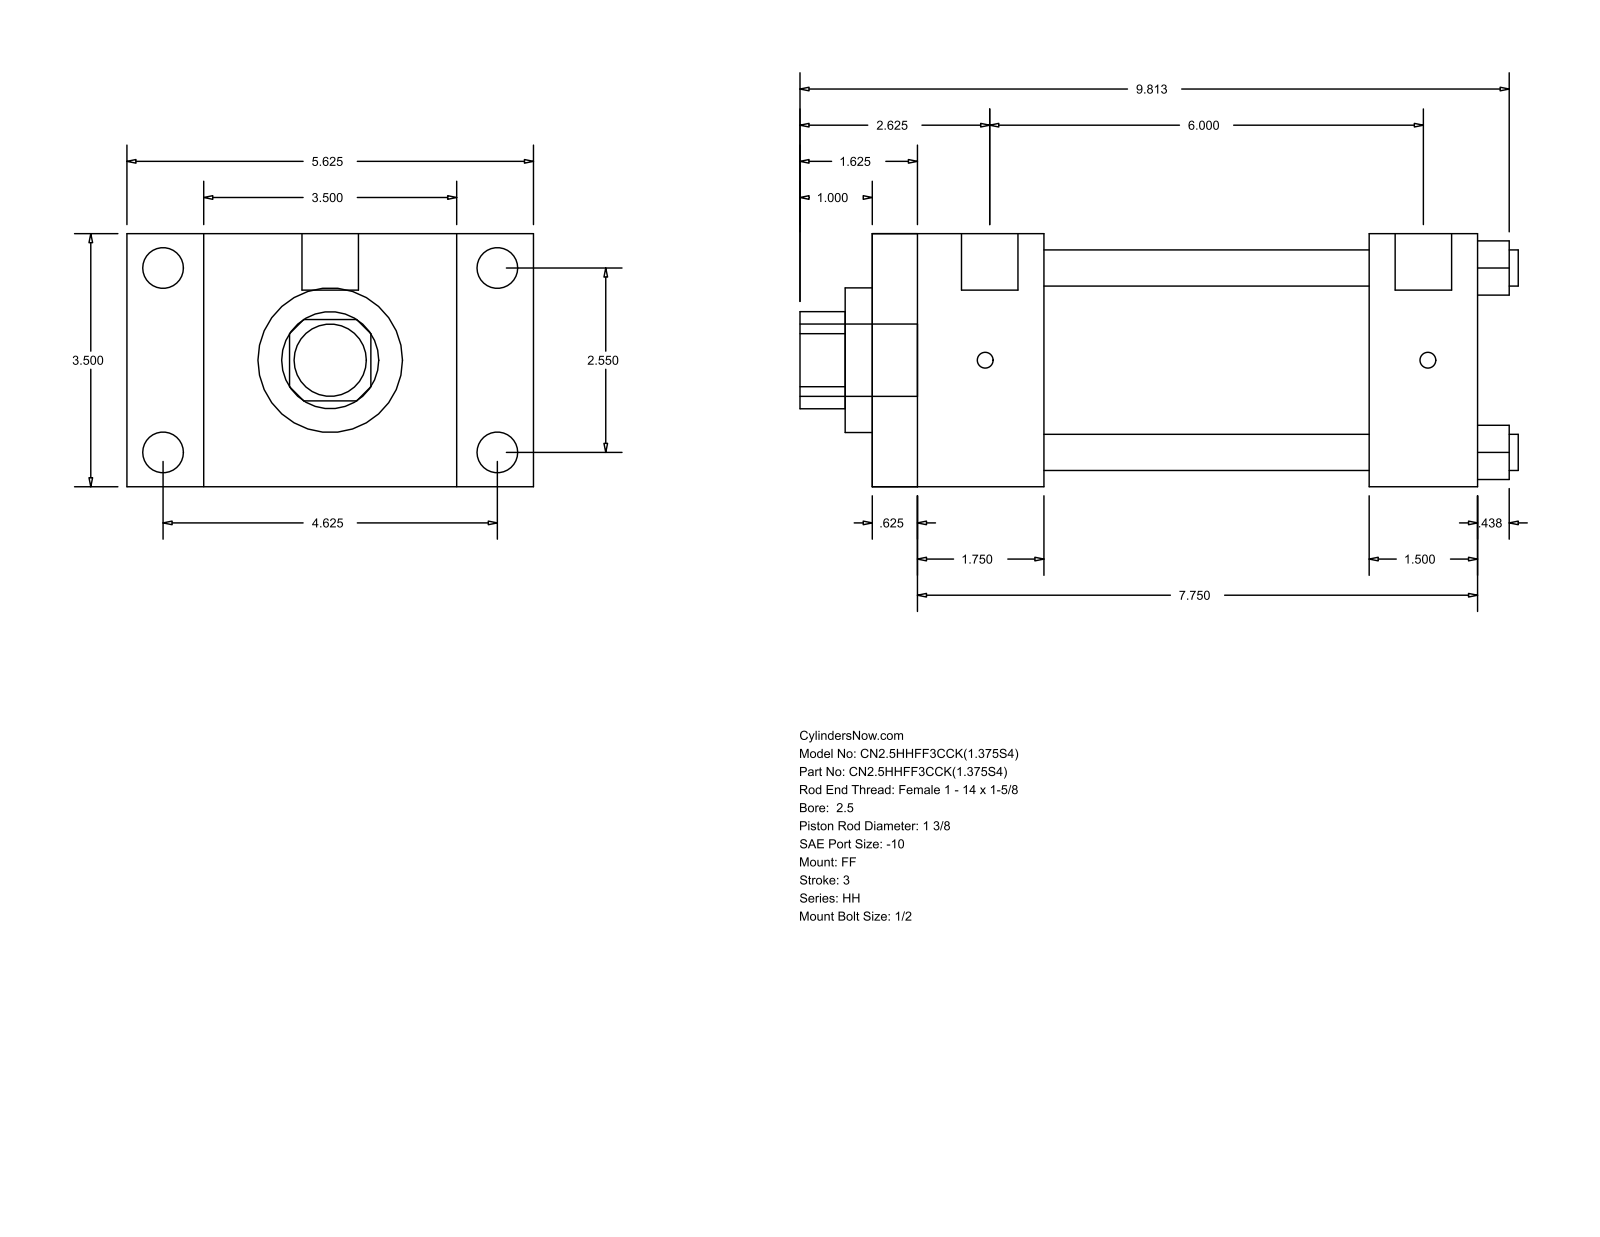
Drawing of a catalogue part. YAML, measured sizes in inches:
part_name: "HH_FF__0250_1.375"
step_written_by: "GSSL Pune (CONFIG_CONTROL_DESIGN)"
units: inches
bodies: {solids: 0, faces: 92, planar: 64, cylindrical: 28, other: 0}
overall_size: [9.937, 5.625, 3.5]
round_holes:
  - {diameter: 0.5, count: 4}
  - {diameter: 1.375, count: 1}
  - {diameter: 2, count: 1}
  - {diameter: 2.875, count: 1}
round_bosses_or_shafts:
  - {diameter: 0.563, count: 4}
  - {diameter: 0.219, count: 4}
  - {diameter: 0.781, count: 2}
  - {diameter: 1, count: 1}
partial_cylinders:
  - {radius: 0.672, count: 1}
face_to_face_distances: [3.5, 8.375, 0.625, 7.75, 2.375, 1.75, 6, 6.875, 6.25, 4.5]
hole_center_spacings: [1.803, 2.55, 3.606]
